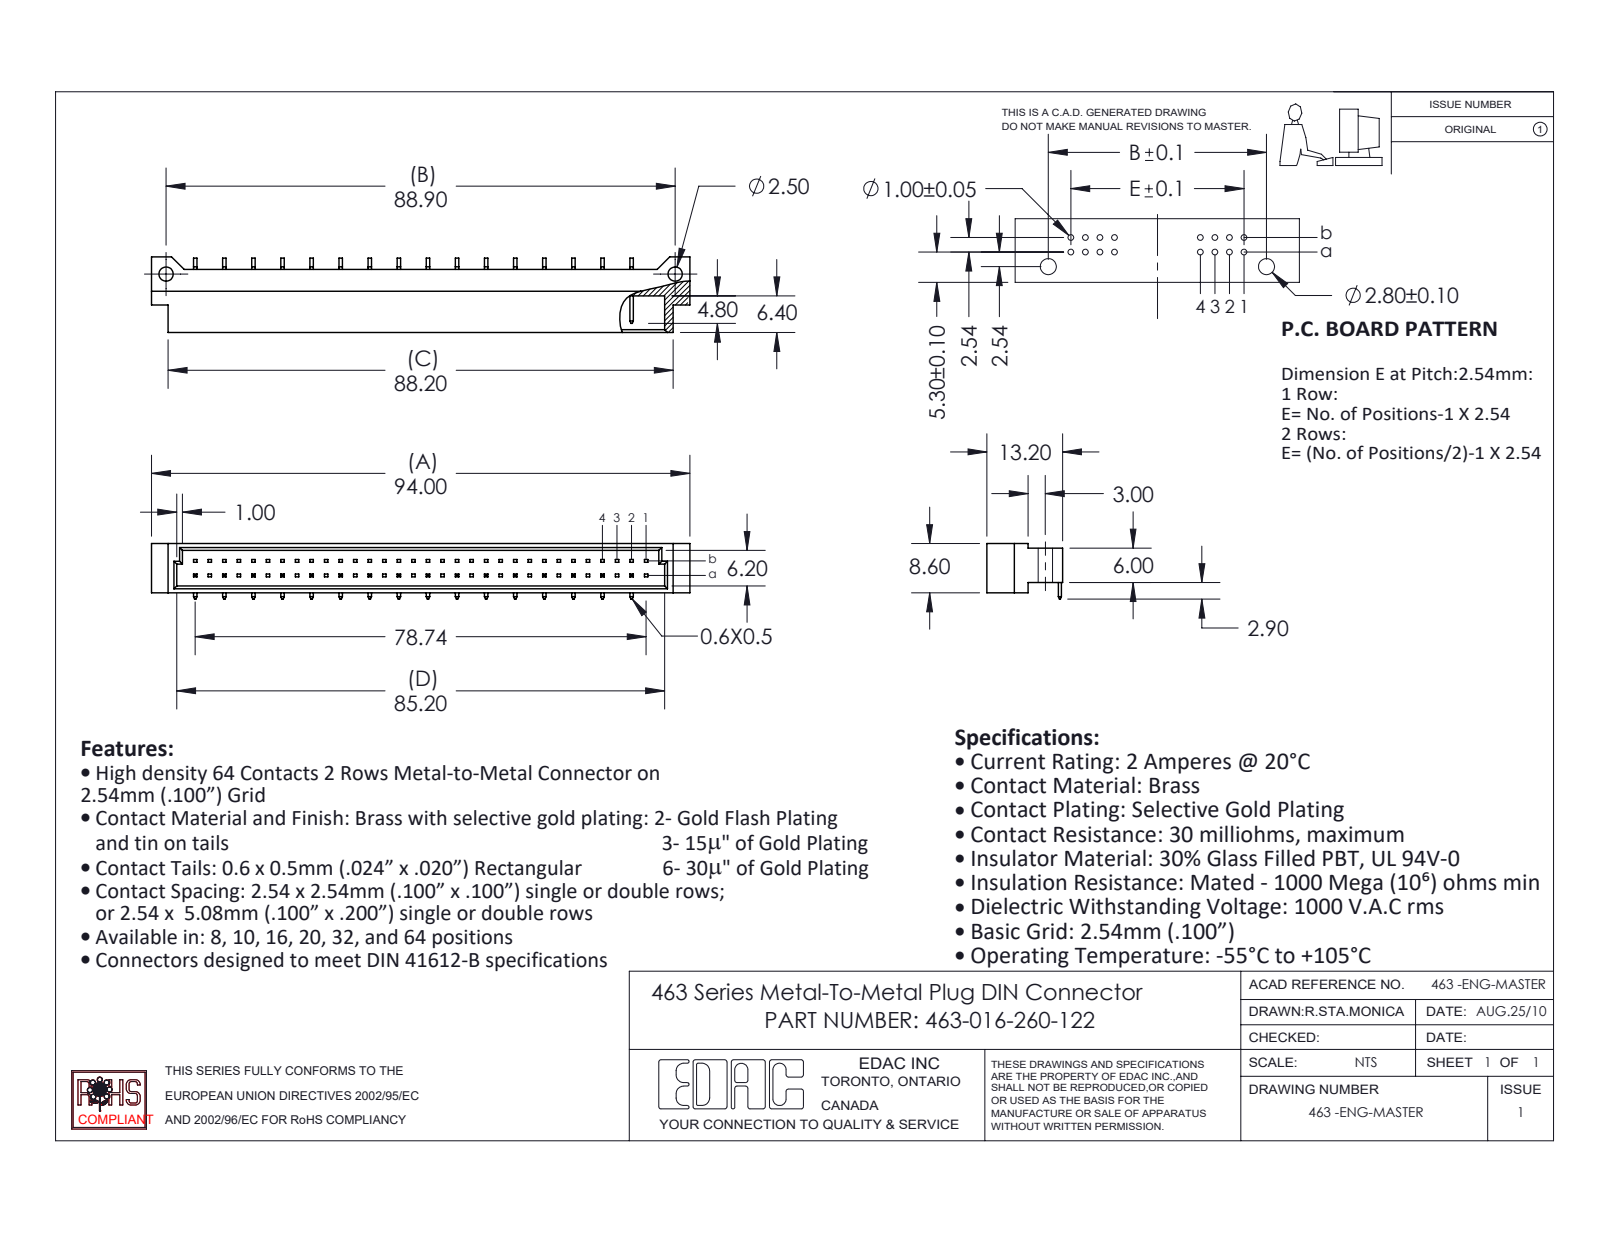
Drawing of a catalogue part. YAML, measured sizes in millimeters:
part_name: "463 Part_64; 463-016-260-122; 463-290-1"
step_written_by: "SolidWorks 2020 (CONFIG_CONTROL_DESIGN)"
units: millimeters
bodies: {solids: 17, faces: 583, planar: 547, cylindrical: 36, other: 0}
overall_size: [94, 13.2, 9.7]
volume: 4394
surface_area: 6188
round_holes:
  - {diameter: 2.5, count: 2}
partial_cylinders:
  - {radius: 1.02, count: 1}
  - {radius: 1.52, count: 1}
face_to_face_distances: [1.2, 7.4, 8.6, 0.8, 6.2, 4.6, 6, 6.8, 5.6, 7.8]
hole_center_spacings: [88.9]
